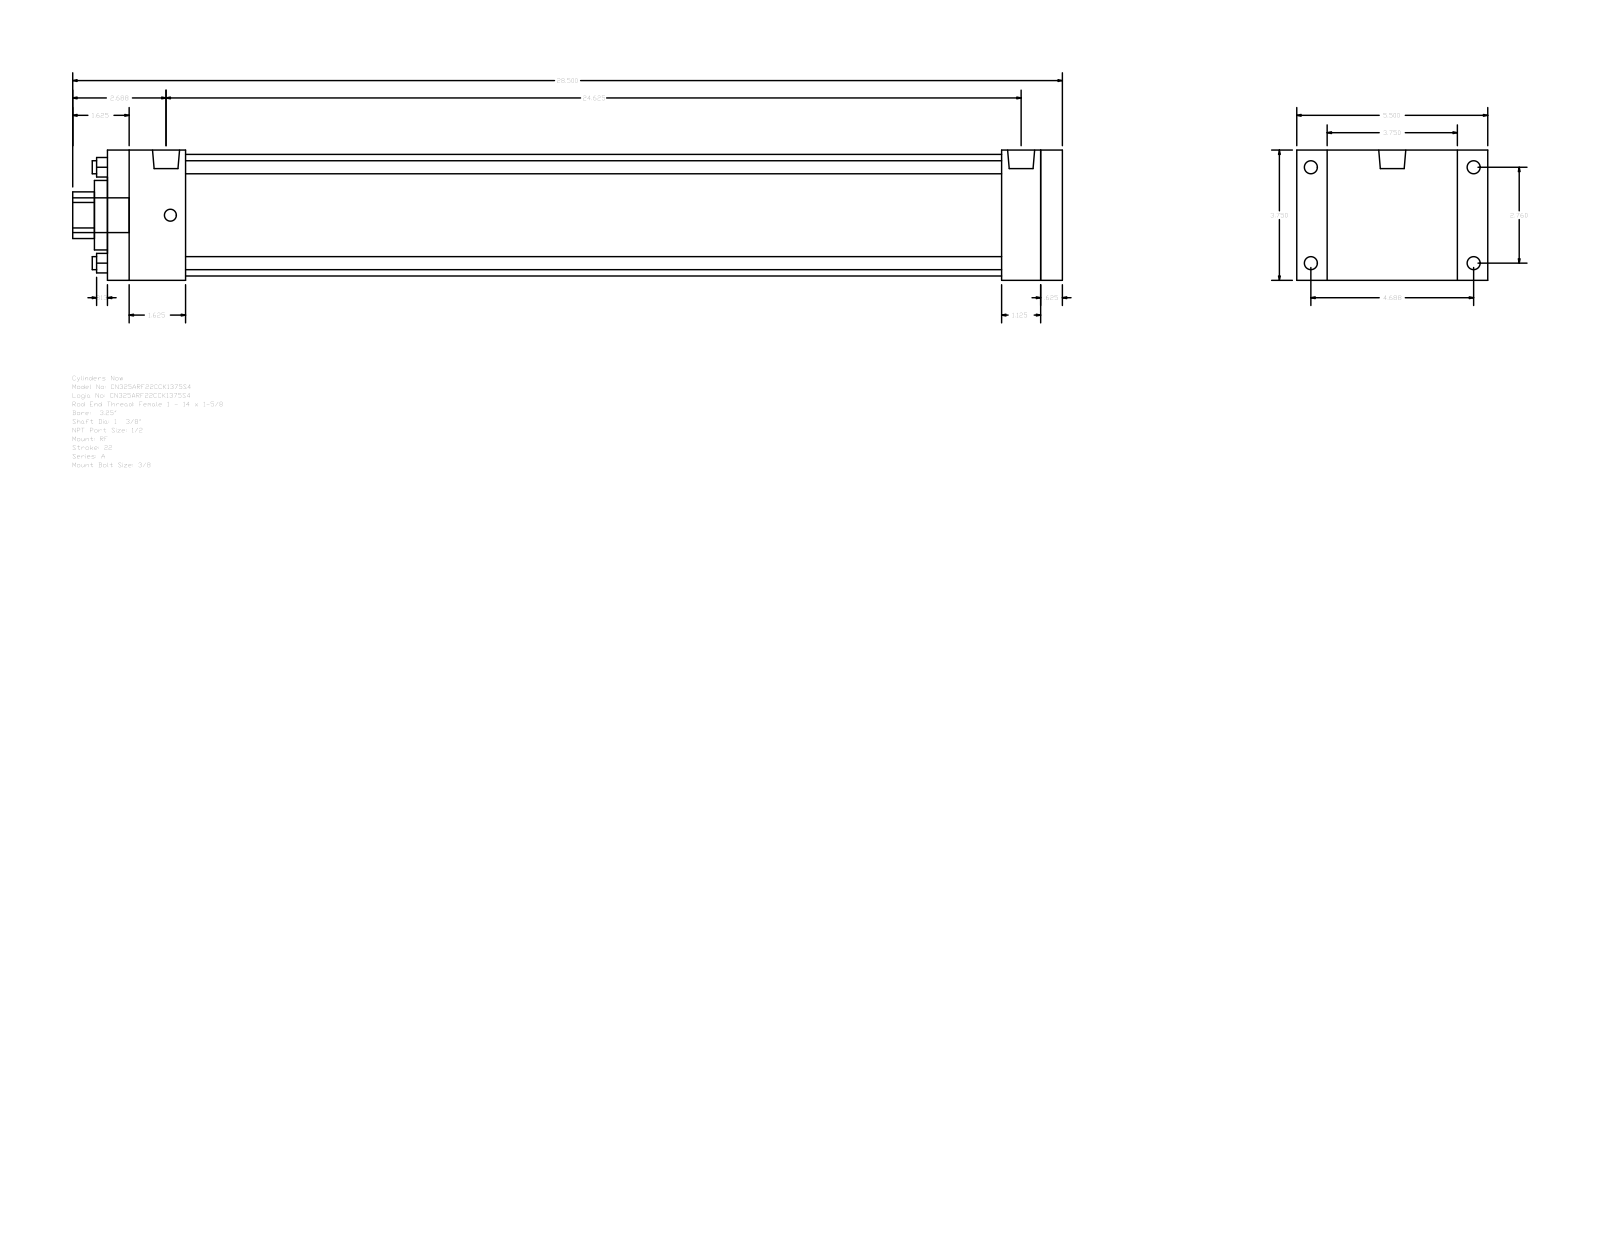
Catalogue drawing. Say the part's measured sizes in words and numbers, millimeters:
The part is named "A_RF__0325_1.375". Its 3-D file was written by "GSSL Pune (CONFIG_CONTROL_DESIGN)". It is 0 solids with 92 faces: 64 planar, 28 cylindrical and 0 other. Overall it measures 723.9 by 139.7 by 95.25 millimeters. Round holes: 4 of diameter 9.53, 1 of diameter 34.92, 1 of diameter 50.8, 1 of diameter 88.9. Round bosses or shafts: 4 of diameter 9.53, 4 of diameter 8.73, 2 of diameter 19.77, 1 of diameter 25.4. Partial cylindrical surfaces (rounded edges, fillets, slot ends): 1 of radius 17.06. The main face-to-face distances are 95.24, 698.5, 15.88, 682.62, 22.23, 117.47, 28.57, 654.05, 44.45, 57.15. The hole center spacings are 49.57, 70.1, 99.14.
